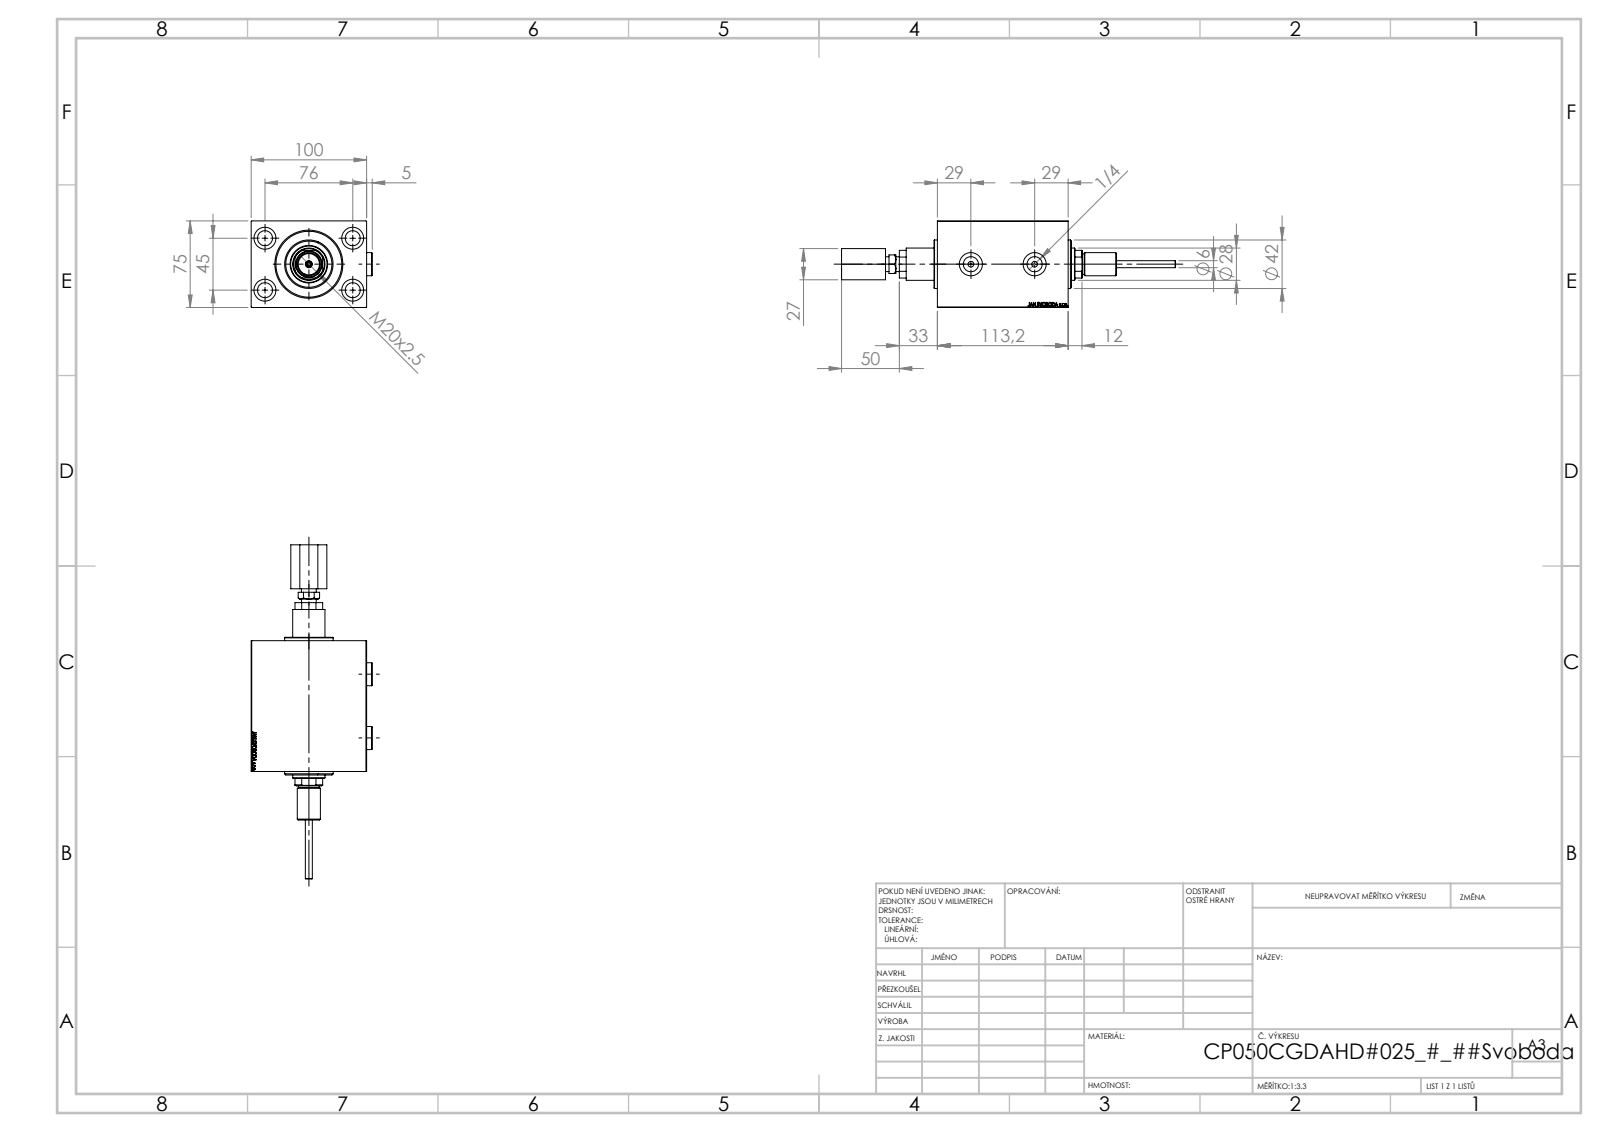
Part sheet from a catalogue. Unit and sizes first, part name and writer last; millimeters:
Units: millimetres
Overall size (bounding box): 289.2 × 104.9 × 75
Round holes (diameter × count): ⌀13 ×4, ⌀19 ×4, ⌀4 ×2, ⌀5 ×2, ⌀9.73 ×2, ⌀13.16 ×2, ⌀15 ×2, ⌀20 ×2, ⌀3 ×1, ⌀6 ×1, ⌀18.5 ×1, ⌀28 ×1
Round bosses / shafts (diameter × count): ⌀42 ×1, ⌀20 ×1, ⌀18 ×1, ⌀12.78 ×1
Partial cylindrical surfaces — rounded edges, fillets, slot ends (radius × count): R13.5 ×1
Main face-to-face distances: 75, 100, 99.2, 113.2, 14, 13, 1, 112.2, 25, 55
Hole centre spacings: 44.16, 45, 76, 88.32, 42.55, 55.2
Volume: 791 358 mm³ · Surface area: 149 284 mm²
Bodies: 7 solids, 1024 faces (480 planar, 122 cylindrical, 422 other)
Part name (STEP PRODUCT): PLUG; V450CP_MALE_METRIC; V450DCP_VC_B; V450DCP_B_RodCooling_ACCESSORIES (+2 more)
STEP written by: SolidWorks 2019 (CONFIG_CONTROL_DESIGN)
